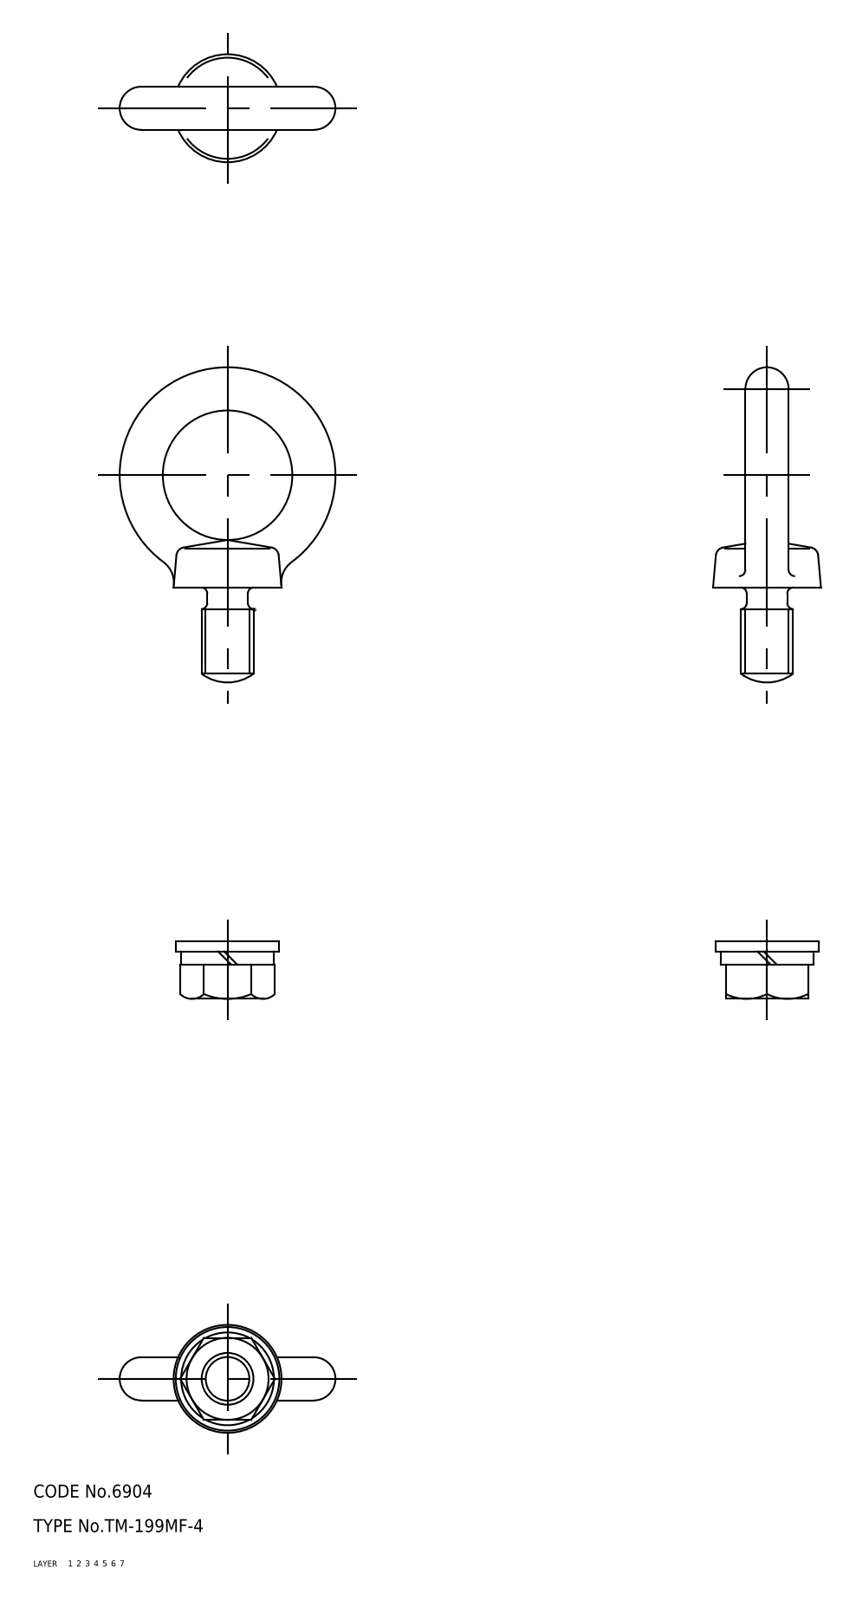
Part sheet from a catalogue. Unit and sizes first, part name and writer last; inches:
Units: inches
Overall size (bounding box): 2.874 × 1.969 × 0.984
Round holes (diameter × count): ⌀0.472 ×1
Round bosses / shafts (diameter × count): ⌀0.945 ×1, ⌀0.846 ×1
Main face-to-face distances: 0.091, 0.118, 0.209, 0.748, 0.315, 0.433, 0.524
Volume: 1.119 in³ · Surface area: 13.15 in²
Bodies: 4 solids, 52 faces (13 planar, 12 cylindrical, 27 other)
Part name (STEP PRODUCT): TM_199MF_4
STEP written by: SolidWorks 2003240 (AUTOMOTIVE_DESIGN)
